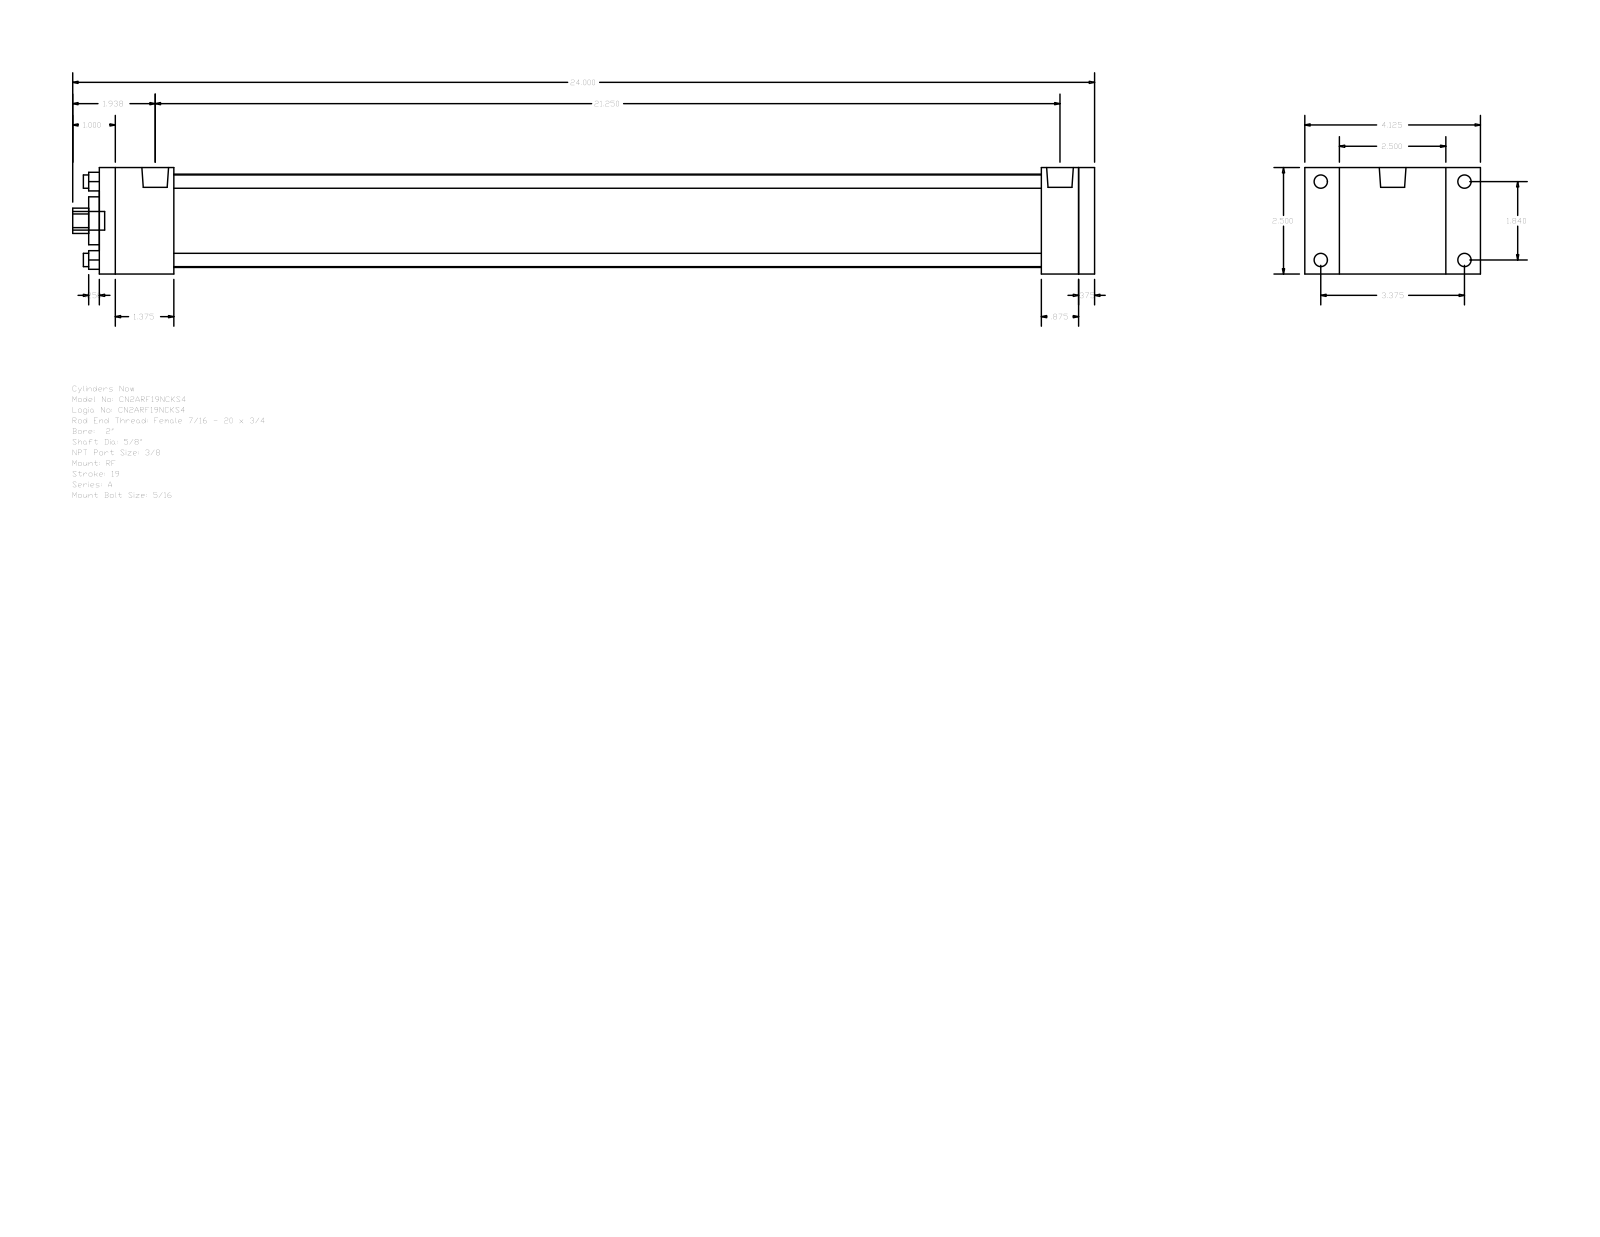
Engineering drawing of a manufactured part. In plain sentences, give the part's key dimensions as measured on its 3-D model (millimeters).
The part is named "A_RF__0200_0.625". Its 3-D file was written by "GSSL Pune (CONFIG_CONTROL_DESIGN)". It is 0 solids with 92 faces: 64 planar, 28 cylindrical and 0 other. Overall it measures 609.6 by 104.78 by 63.5 millimeters. Round holes: 4 of diameter 7.94, 1 of diameter 15.88, 1 of diameter 28.57, 1 of diameter 55.63. Round bosses or shafts: 4 of diameter 7.94, 4 of diameter 5.56, 2 of diameter 15.93, 1 of diameter 11.11. Partial cylindrical surfaces (rounded edges, fillets, slot ends): 1 of radius 7.54. The main face-to-face distances are 63.5, 593.72, 9.52, 584.2, 44.45, 539.75, 549.27, 561.97, 517.52, 22.23. The hole center spacings are 33.05, 46.74, 66.1.
